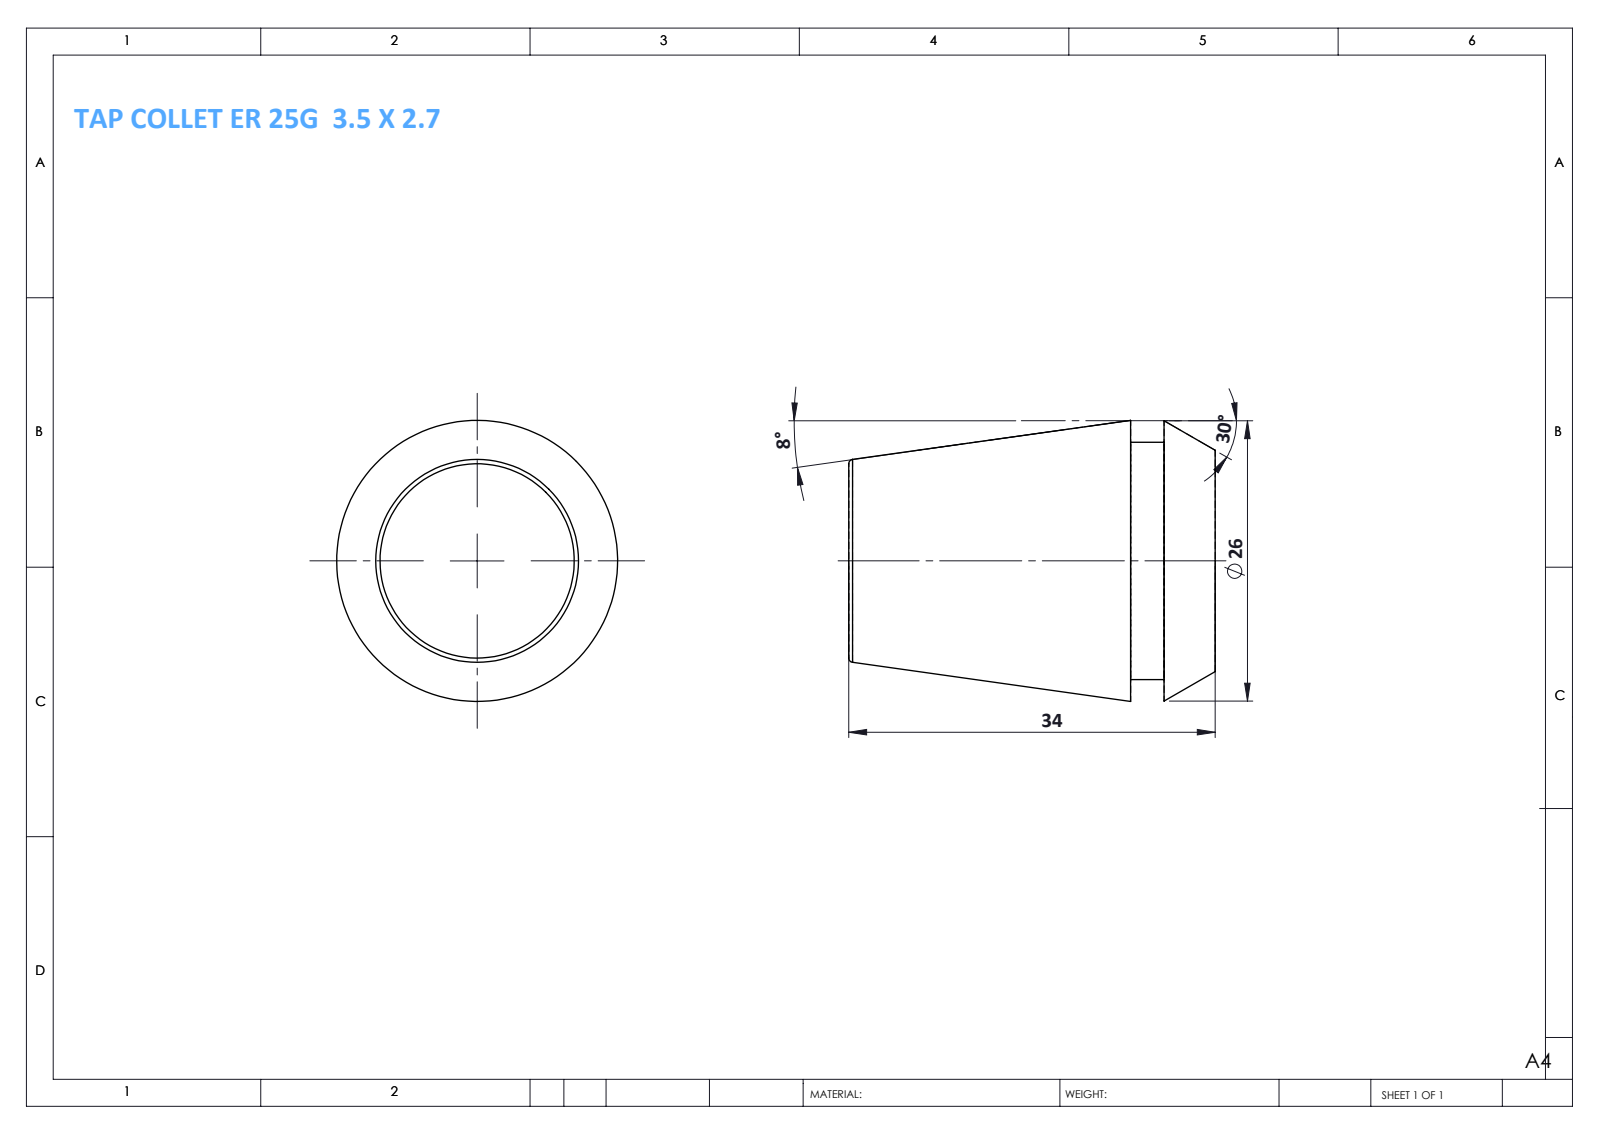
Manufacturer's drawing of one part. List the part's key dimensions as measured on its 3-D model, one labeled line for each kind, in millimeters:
Part name (STEP PRODUCT): TAP COLLET ER 25G 3.5 X 2.7
STEP written by: SolidWorks 2014 (CONFIG_CONTROL_DESIGN)
Units: millimetres
Bodies: 1 solid, 12 faces (4 planar, 2 cylindrical, 6 other)
Overall size (bounding box): 34 × 26.07 × 26.07
Volume: 13 600 mm³ · Surface area: 3 376 mm²
Round bosses / shafts (diameter × count): ⌀22 ×1
Main face-to-face distances: 34, 7.84, 26.16, 4.74, 3.1, 29.26
